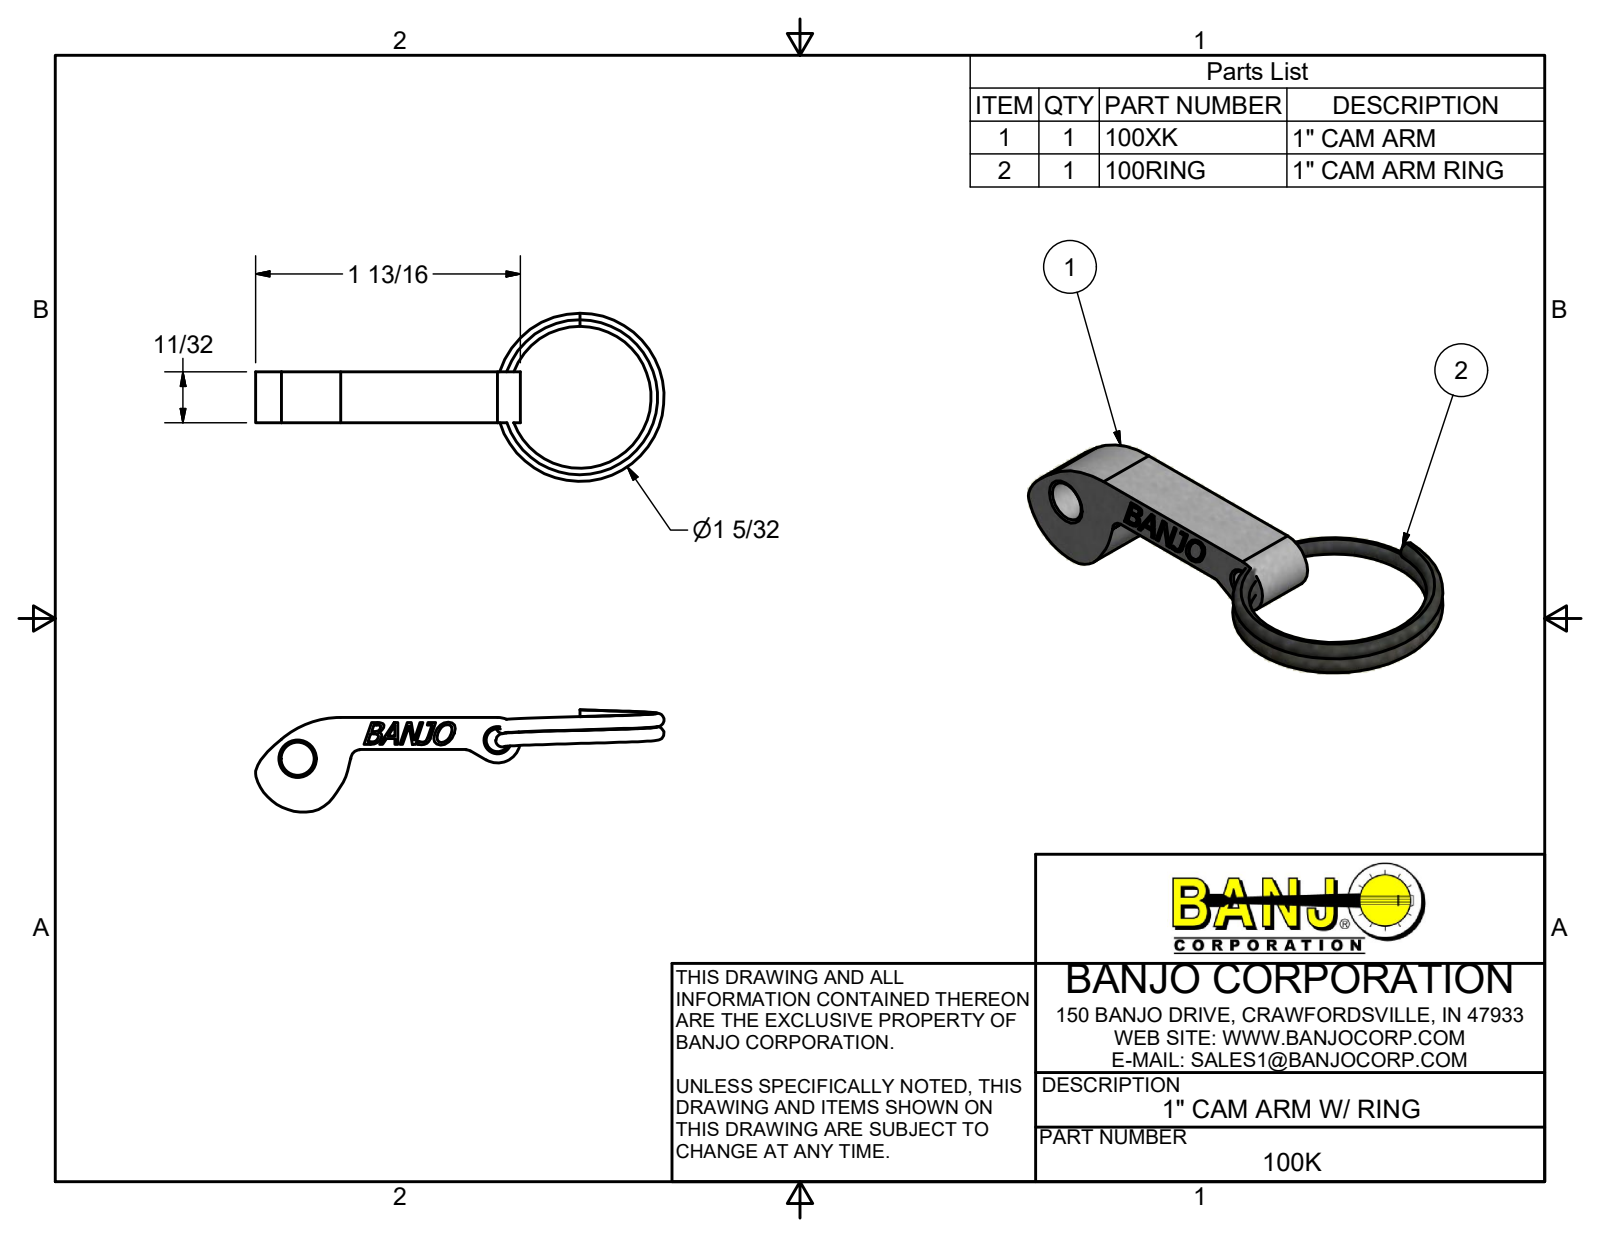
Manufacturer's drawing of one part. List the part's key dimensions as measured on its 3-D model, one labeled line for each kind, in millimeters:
Part name (STEP PRODUCT): 100K; 100XK; 100RING
STEP written by: Autodesk Inventor 2017 (AUTOMOTIVE_DESIGN)
Units: millimetres
Bodies: 2 solids, 177 faces (98 planar, 6 cylindrical, 73 other)
Overall size (bounding box): 71.34 × 29.37 × 17.85
Volume: 3 605 mm³ · Surface area: 3 107 mm²
Round holes (diameter × count): ⌀3.96 ×1, ⌀5.71 ×1
Partial cylindrical surfaces — rounded edges, fillets, slot ends (radius × count): R1.59 ×1, R1.59 ×1, R3.97 ×1, R15.88 ×1
Main face-to-face distances: 8.88, 5.61, 0.5, 8.38, 7.88, 0.9, 4.71, 4.42, 3.92, 3.96
Hole centre spacings: 35.07
